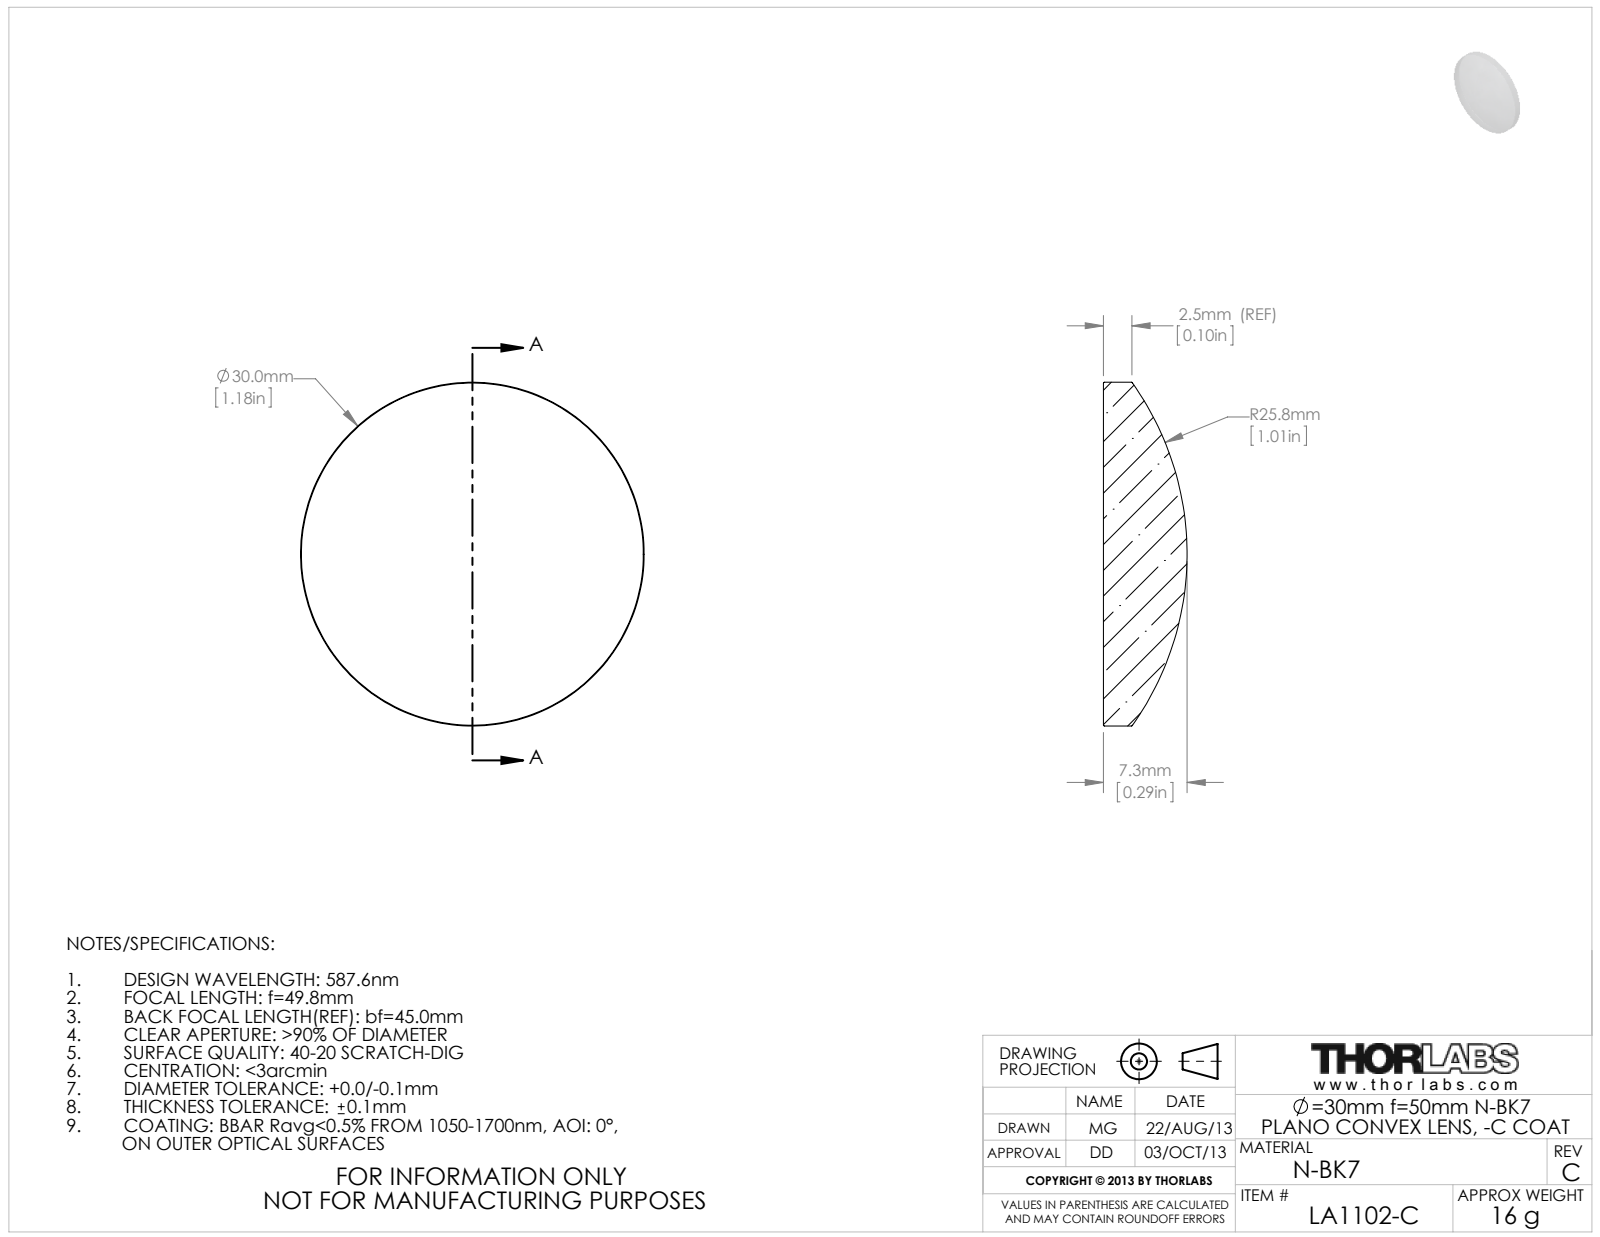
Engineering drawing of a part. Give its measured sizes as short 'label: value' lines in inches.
name: 4596-E0W
written by: SolidWorks 2009 (AUTOMOTIVE_DESIGN)
unit: in
bodies: 1 solid, 5 faces (1 planar, 2 cylindrical, 2 other)
size: 1.181 × 1.181 × 0.288
volume: 0.215 in³; area: 2.668 in²
bosses: 1× ⌀1.181
